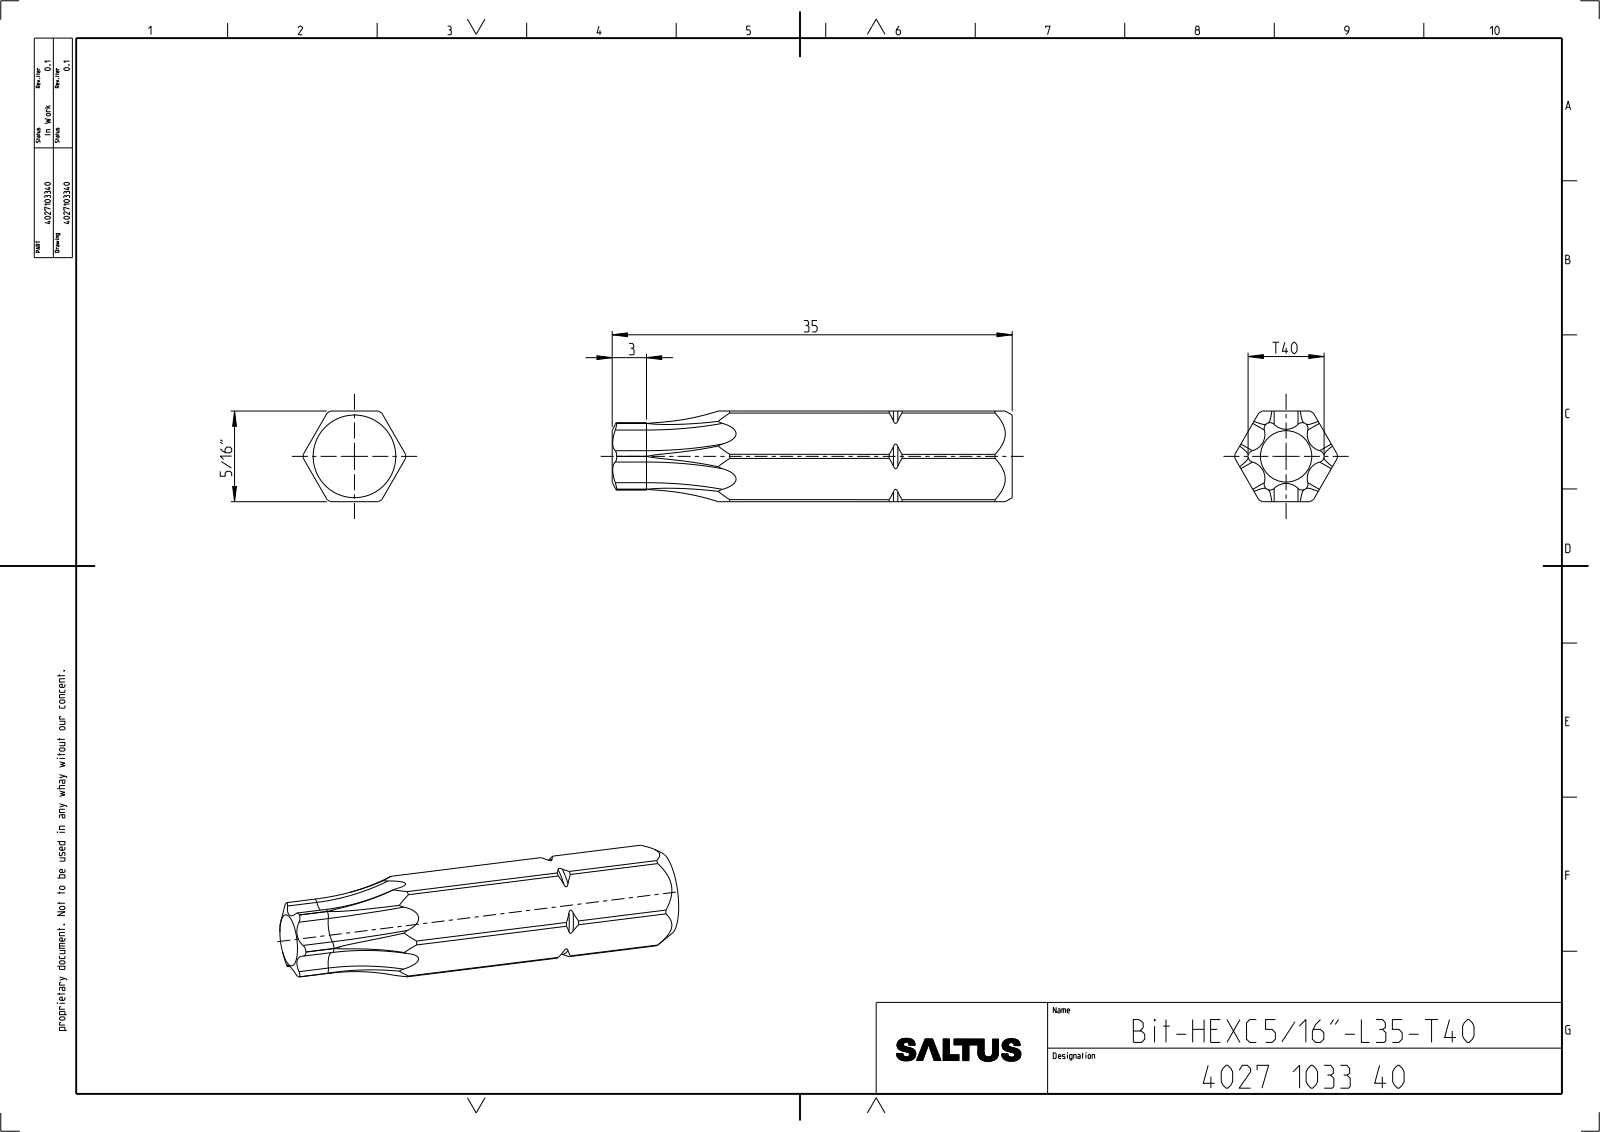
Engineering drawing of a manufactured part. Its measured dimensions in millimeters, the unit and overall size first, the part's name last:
Units: millimetres
Overall size (bounding box): 35 × 8.96 × 7.93
Partial cylindrical surfaces — rounded edges, fillets, slot ends (radius × count): R0.51 ×10, R1.47 ×6, R3.33 ×1, R4.48 ×1
Main face-to-face distances: 7.92, 7.94, 35
Volume: 1 653 mm³ · Surface area: 981 mm²
Bodies: 1 solid, 90 faces (8 planar, 36 cylindrical, 46 other)
Part name (STEP PRODUCT): 4027103340
STEP written by: CREO PARAMETRIC BY PTC INC, 2022414 (CONFIG_CONTROL_DESIGN)
